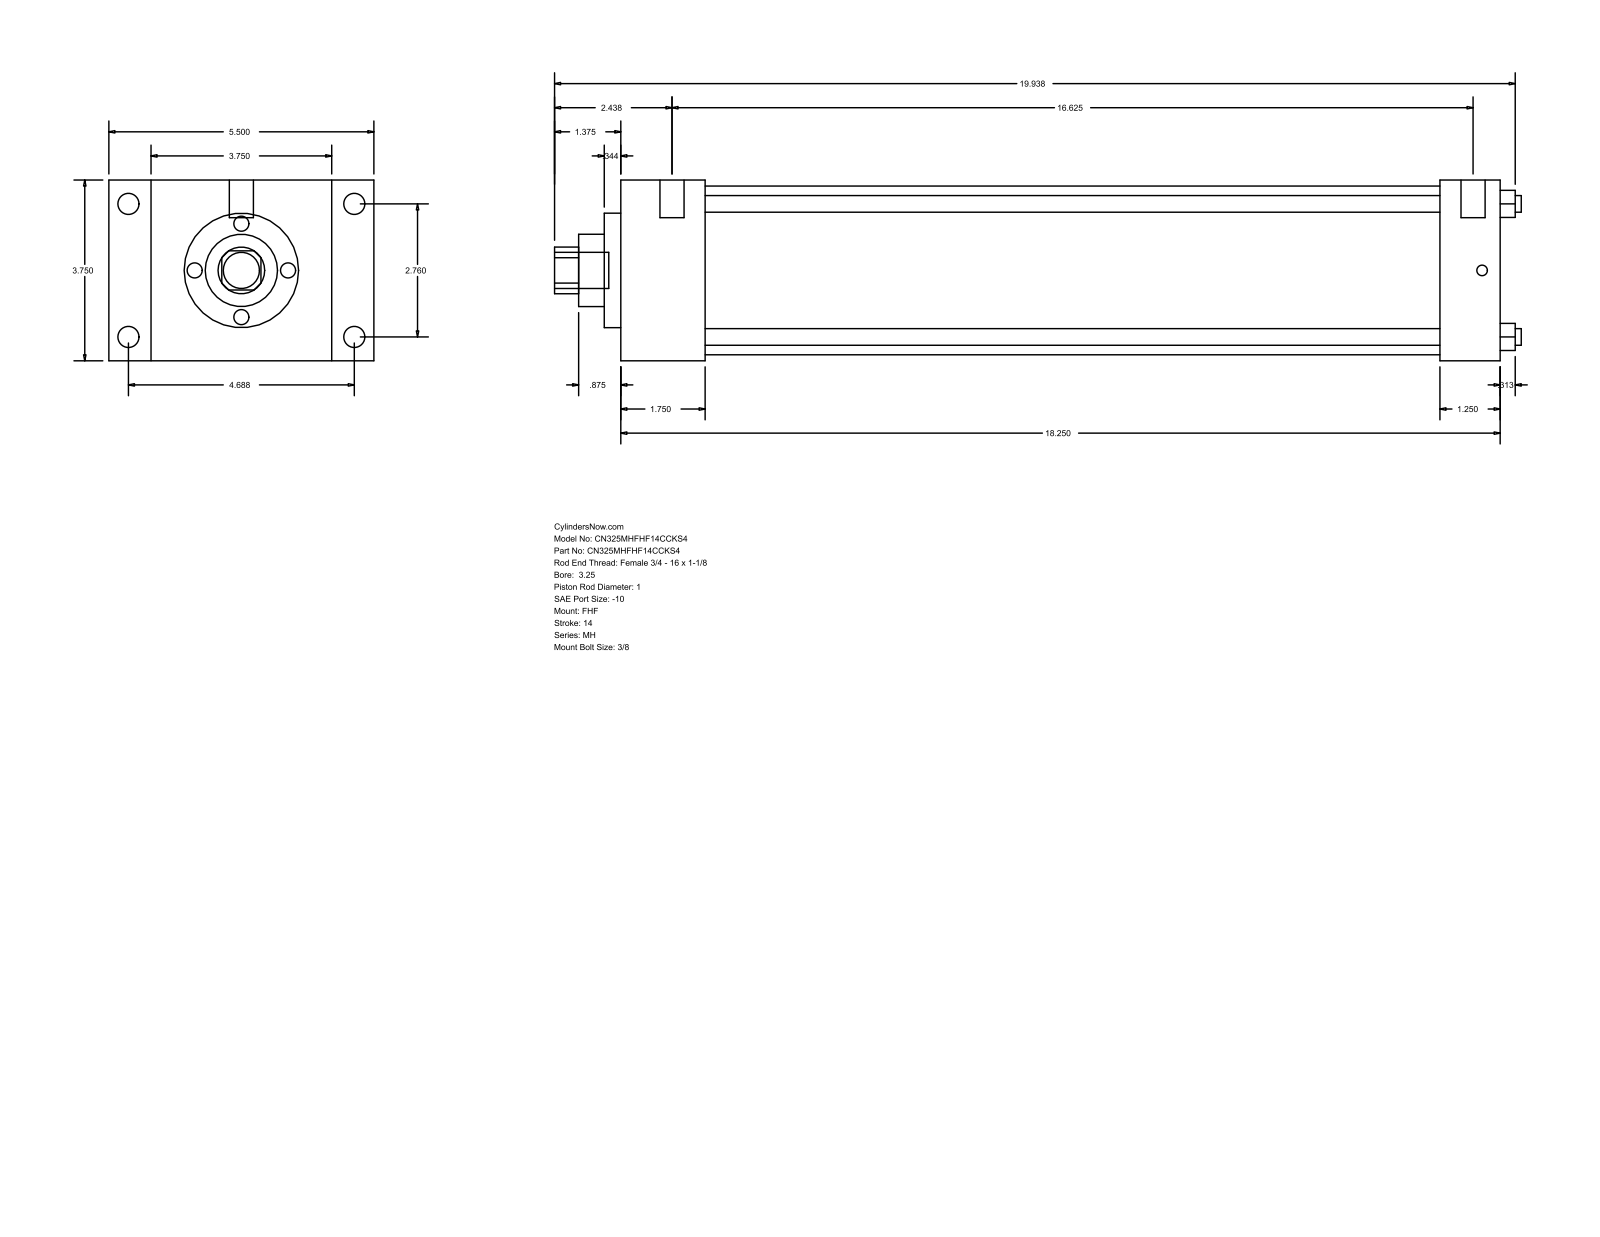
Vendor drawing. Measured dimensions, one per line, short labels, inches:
name: MH_FHF__0325_1
written by: GSSL Pune (CONFIG_CONTROL_DESIGN)
unit: in
bodies: 0 solids, 90 faces (61 planar, 29 cylindrical, 0 other)
size: 20.063 × 5.5 × 3.75
holes: 4× ⌀0.345, 1× ⌀1, 1× ⌀1.5, 1× ⌀2.375, 1× ⌀3.5
bosses: 4× ⌀0.438, 4× ⌀0.219, 2× ⌀0.5, 1× ⌀0.75
rounds: 1× R0.484
face distances: 3.75, 18.25, 1.75, 16.5, 0.875, 4.625, 5.5, 17, 15.25, 1.25
hole spacings: 1.952, 2.76, 3.903
